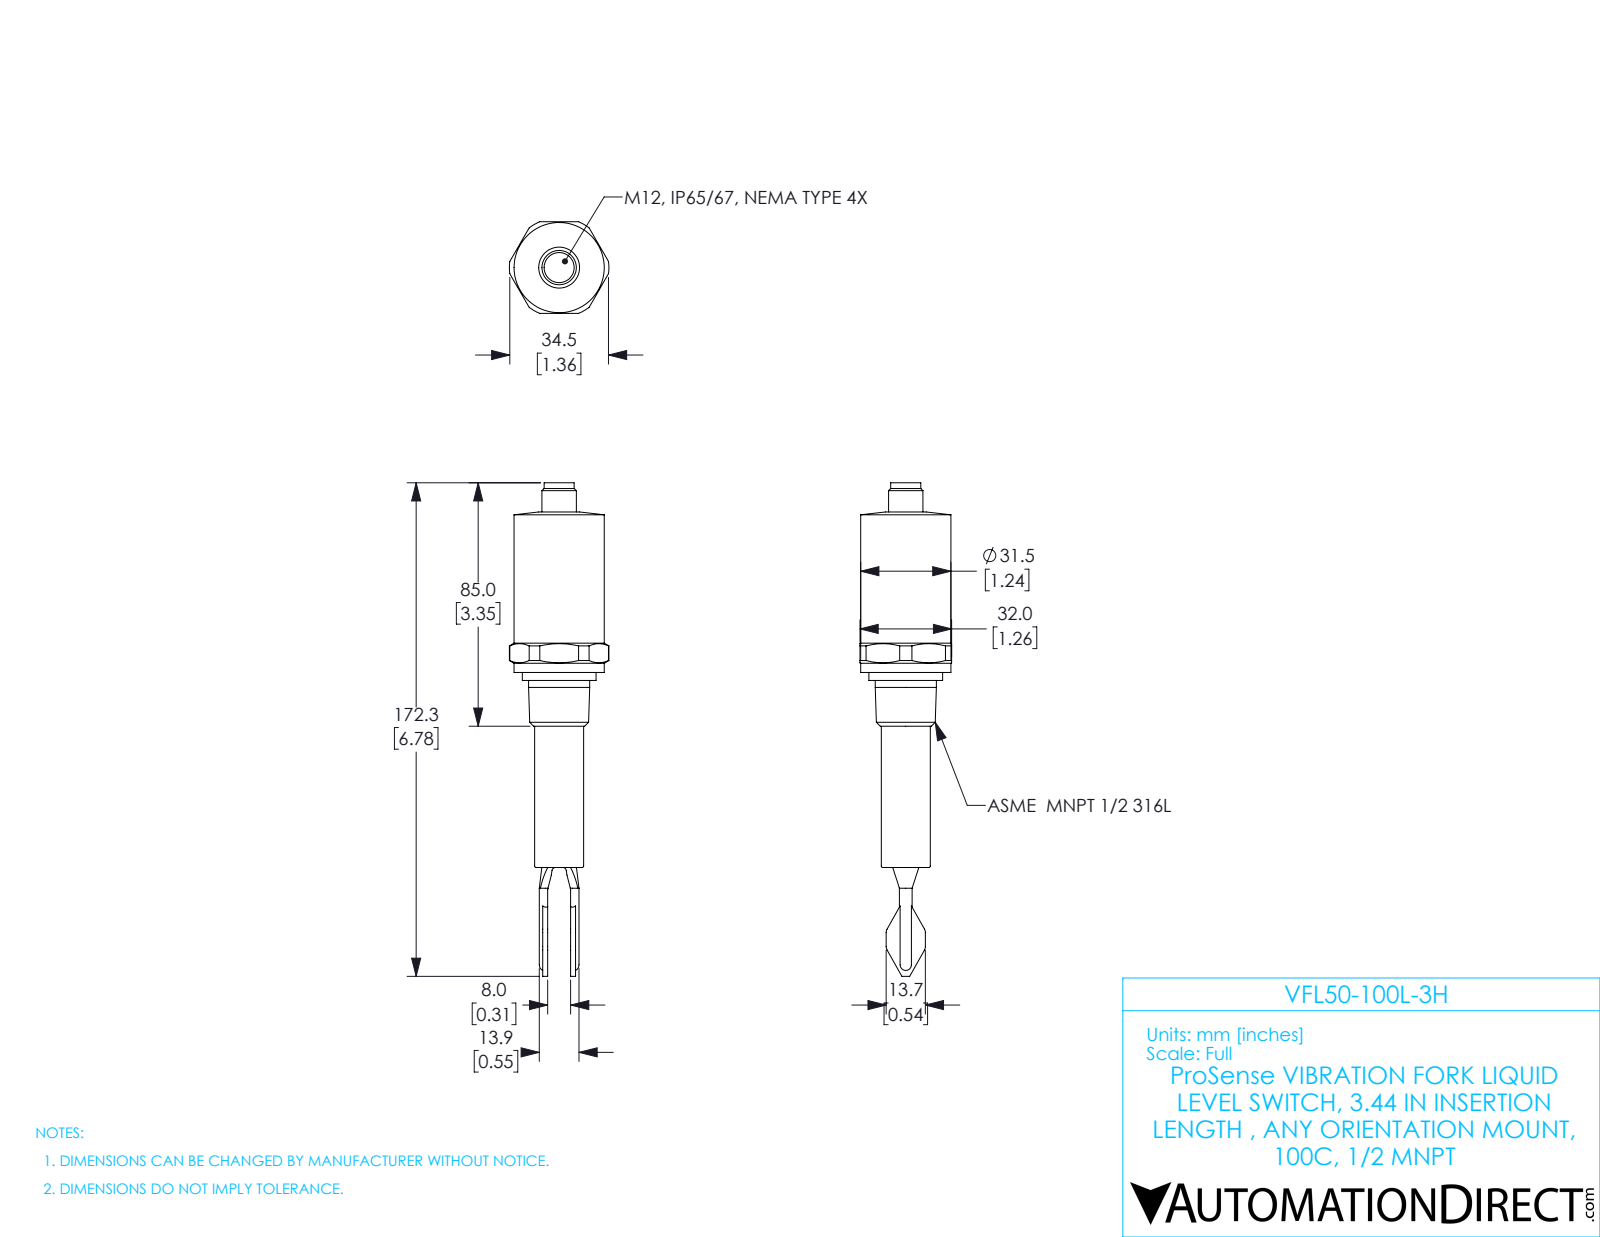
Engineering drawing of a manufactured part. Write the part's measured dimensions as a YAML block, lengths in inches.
part_name: "VFL50-100L-3H"
step_written_by: "SolidWorks 2017 (AUTOMOTIVE_DESIGN)"
units: inches
bodies: {solids: 1, faces: 101, planar: 46, cylindrical: 36, other: 19}
overall_size: [6.783, 1.368, 1.26]
volume: 3.945
surface_area: 20.06
round_bosses_or_shafts:
  - {diameter: 1.24, count: 1}
  - {diameter: 1.014, count: 1}
  - {diameter: 0.84, count: 1}
  - {diameter: 0.673, count: 1}
  - {diameter: 0.472, count: 1}
  - {diameter: 0.413, count: 1}
partial_cylinders:
  - {radius: 0.047, count: 4}
  - {radius: 0.094, count: 4}
  - {radius: 0.088, count: 2}
  - {radius: 0.684, count: 1}
face_to_face_distances: [0.068, 0.383, 0.315, 1.26, 0.11, 0.451, 2.571, 2.681, 5.287, 2.717]
